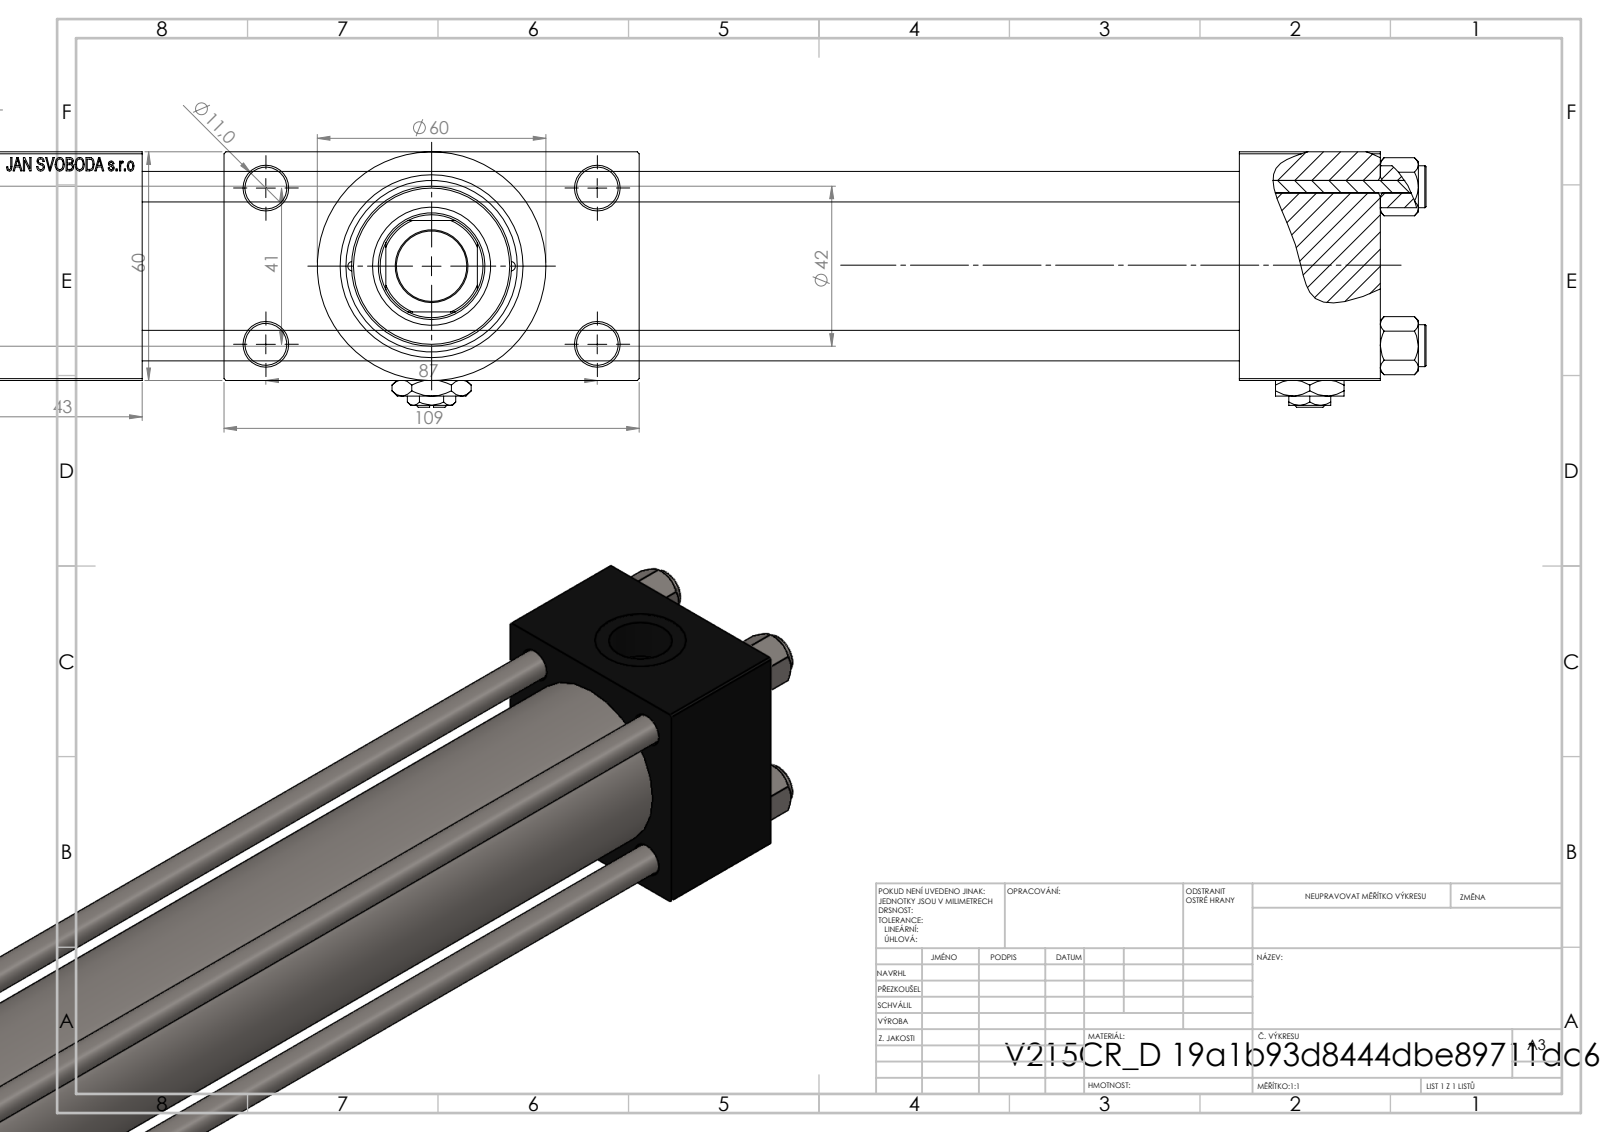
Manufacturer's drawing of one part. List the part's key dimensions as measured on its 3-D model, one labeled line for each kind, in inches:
Part name (STEP PRODUCT): V215CR_D_Body; V215_VC_A; Zatka_pro_OIL_PORT; V215CR_VCP_D (+2 more)
STEP written by: SolidWorks 2019 (CONFIG_CONTROL_DESIGN)
Units: inches
Bodies: 12 solids, 1168 faces (526 planar, 100 cylindrical, 542 other)
Overall size (bounding box): 16.339 × 4.291 × 2.638
Volume: 49.63 in³ · Surface area: 364.3 in²
Round holes (diameter × count): ⌀0.315 ×4, ⌀0.433 ×4, ⌀0.098 ×2, ⌀0.276 ×2, ⌀0.656 ×2, ⌀0.945 ×2, ⌀0.728 ×1, ⌀1.102 ×1, ⌀1.22 ×1, ⌀1.575 ×1, ⌀1.772 ×1
Round bosses / shafts (diameter × count): ⌀0.433 ×4, ⌀2.362 ×1, ⌀1.811 ×1, ⌀1.654 ×1
Partial cylindrical surfaces — rounded edges, fillets, slot ends (radius × count): R0.531 ×1
Main face-to-face distances: 2.362, 0.965, 3.327, 11.339, 1.457, 12.795, 14.488, 13.031, 1.693, 4.291
Hole centre spacings: 0.821, 0.892, 1.161, 1.206, 1.642, 1.832, 1.856, 1.893
